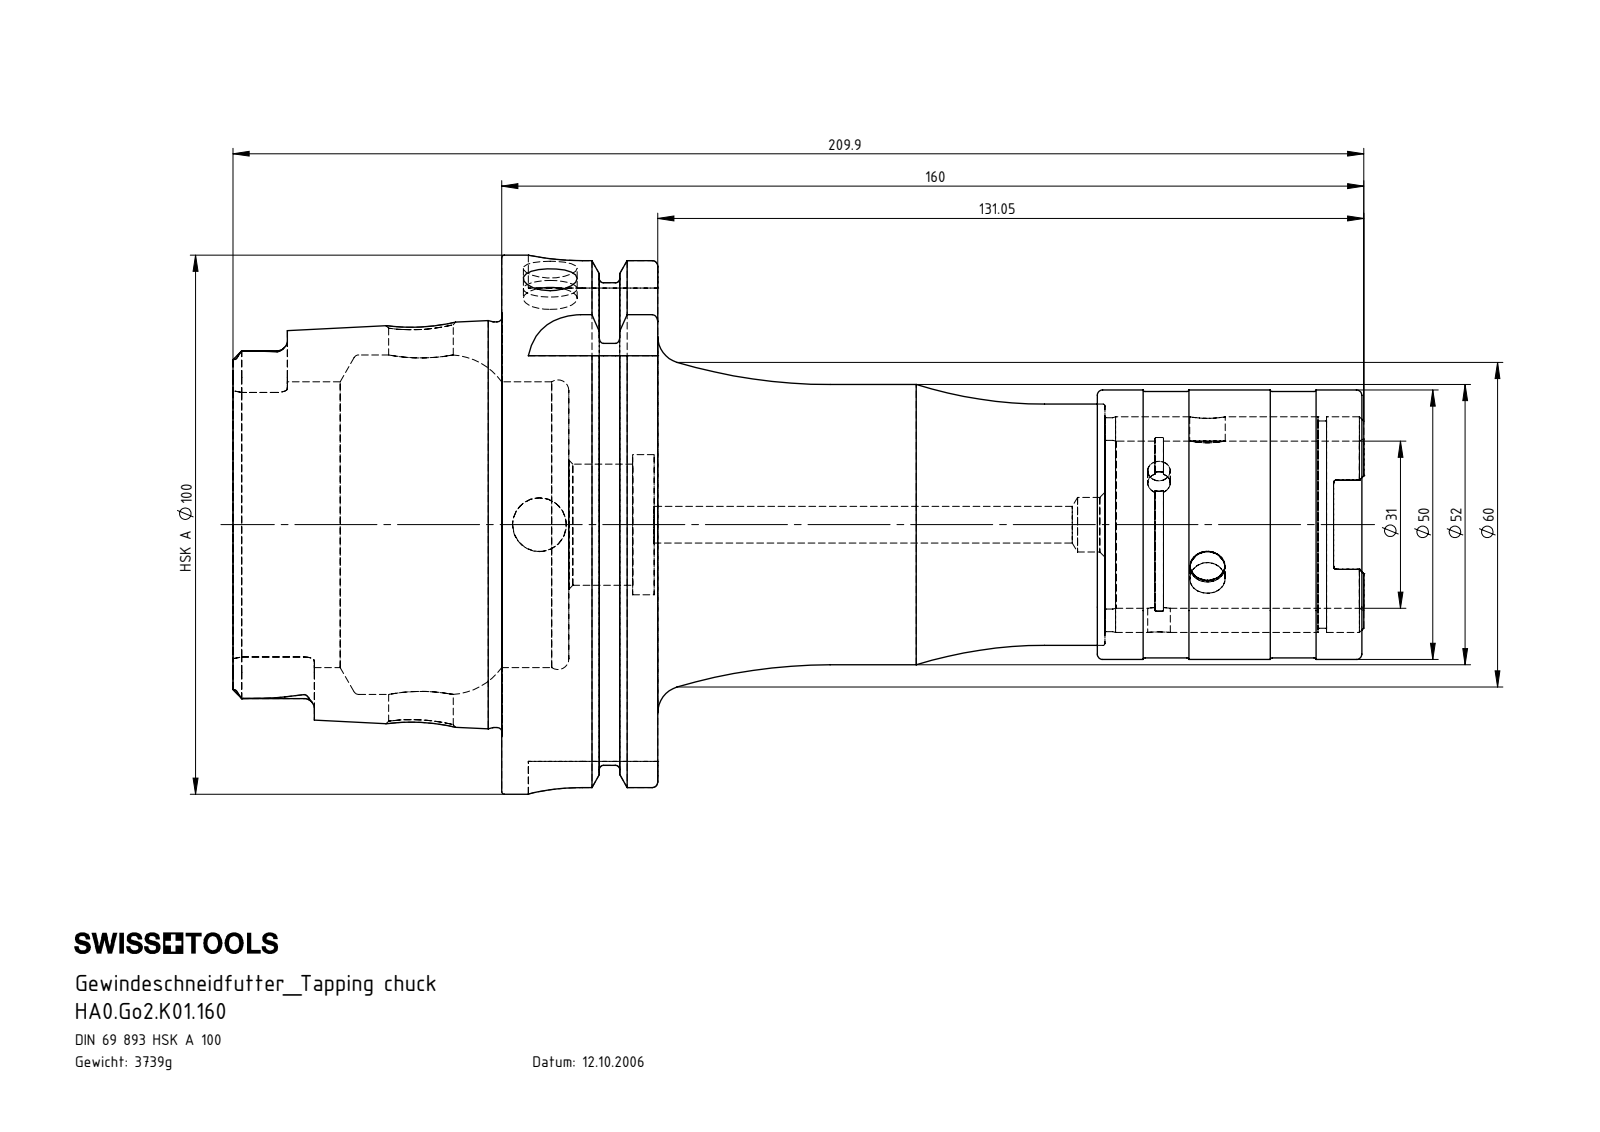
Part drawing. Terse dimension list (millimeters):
name: HA0.Go2.K01.160; Einbausatz Go2_gespannt; Kugel Go2; Hülse Go2 (+6 more)
written by: SolidWorks 2011 (AUTOMOTIVE_DESIGN)
unit: mm
bodies: 10 solids, 377 faces (83 planar, 122 cylindrical, 172 other)
size: 209.9 × 100 × 100
volume: 476 232 mm³; area: 97 704 mm²
holes: 3× ⌀4.2, 3× ⌀6.6, 3× ⌀10, 1× ⌀2.5, 1× ⌀6.8, 1× ⌀10.1, 1× ⌀12, 1× ⌀22.5, 1× ⌀26, 1× ⌀31, 1× ⌀31.3, 1× ⌀32.35
bosses: 1× ⌀100, 1× ⌀91.95, 1× ⌀75.26, 1× ⌀52, 1× ⌀50, 1× ⌀49.4, 1× ⌀44.75, 1× ⌀40
rounds: 6× R1.9, 4× R4.88, 4× R10, 3× R3.1, 2× R0.5
face distances: 28.95, 12.45, 16.5, 0.65, 83.7, 49.9, 62.35, 78.85, 174.55, 124.65
hole spacings: 9, 137, 146
